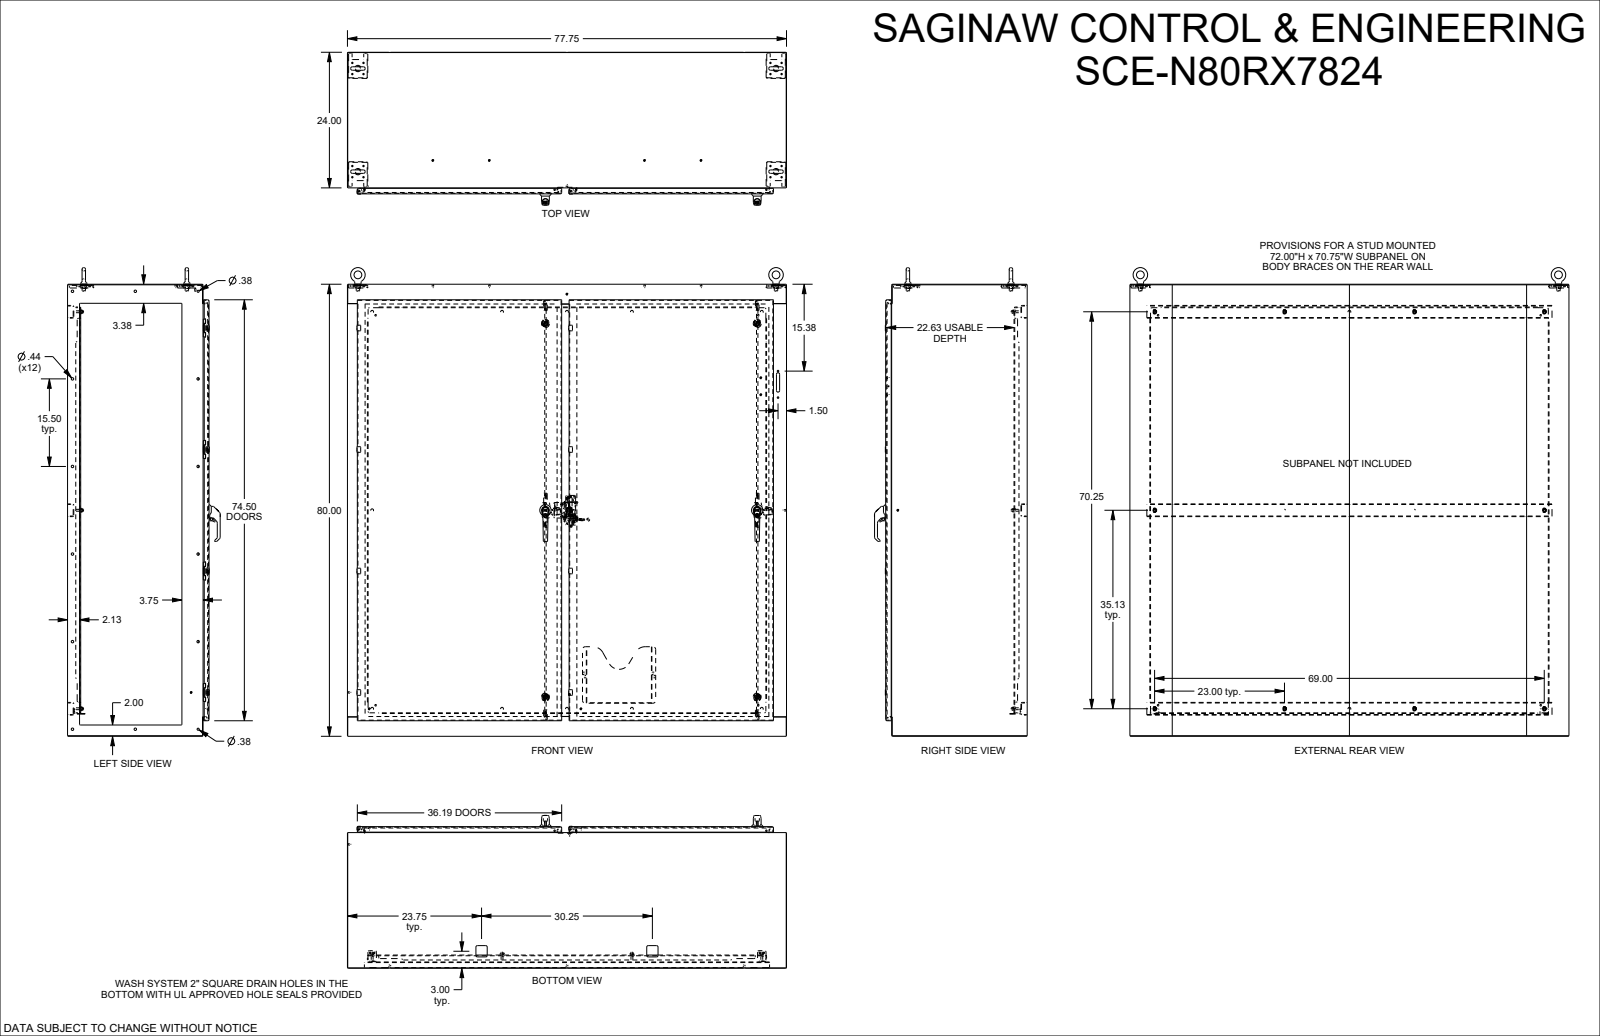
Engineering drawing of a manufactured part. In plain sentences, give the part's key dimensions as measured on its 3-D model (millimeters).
The part is named "SCE-N80RX7824_REV1". Its 3-D file was written by "SolidWorks 2023 (AUTOMOTIVE_DESIGN)". It is 51 solids with 7624 faces: 3127 planar, 2609 cylindrical and 1888 other. Overall it measures 2106.8 by 1974.9 by 687 millimeters. Its volume is 37 850 000 cubic millimeters and its surface area 28 380 000 square millimeters. Round holes: 22 of diameter 6.4, 16 of diameter 6.2, 16 of diameter 9.5, 14 of diameter 11.2, 8 of diameter 1, 8 of diameter 4.3, 8 of diameter 5.2, 8 of diameter 5.2, 8 of diameter 5.5, 4 of diameter 6.5, 4 of diameter 8.7, 4 of diameter 8.7. Round bosses or shafts: 24 of diameter 4.3, 19 of diameter 6.4, 16 of diameter 6.1, 10 of diameter 5, 4 of diameter 35.6, 4 of diameter 29.8, 4 of diameter 15.2, 4 of diameter 8.7. Partial cylindrical surfaces (rounded edges, fillets, slot ends): 215 of radius 0.8, 166 of radius 0.4, 96 of radius 3.2, 65 of radius 0.5, 59 of radius 1, 48 of radius 0.5, 46 of radius 1, 44 of radius 1.6. The main face-to-face distances are 2.6, 633.8, 631.2, 636.5, 2029.4, 607, 26.9, 2032, 2026.7, 604.3. The hole center spacings are 546.1, 50.3, 952.5, 393.7, 688.8, 35.6, 787.4, 969.2.
